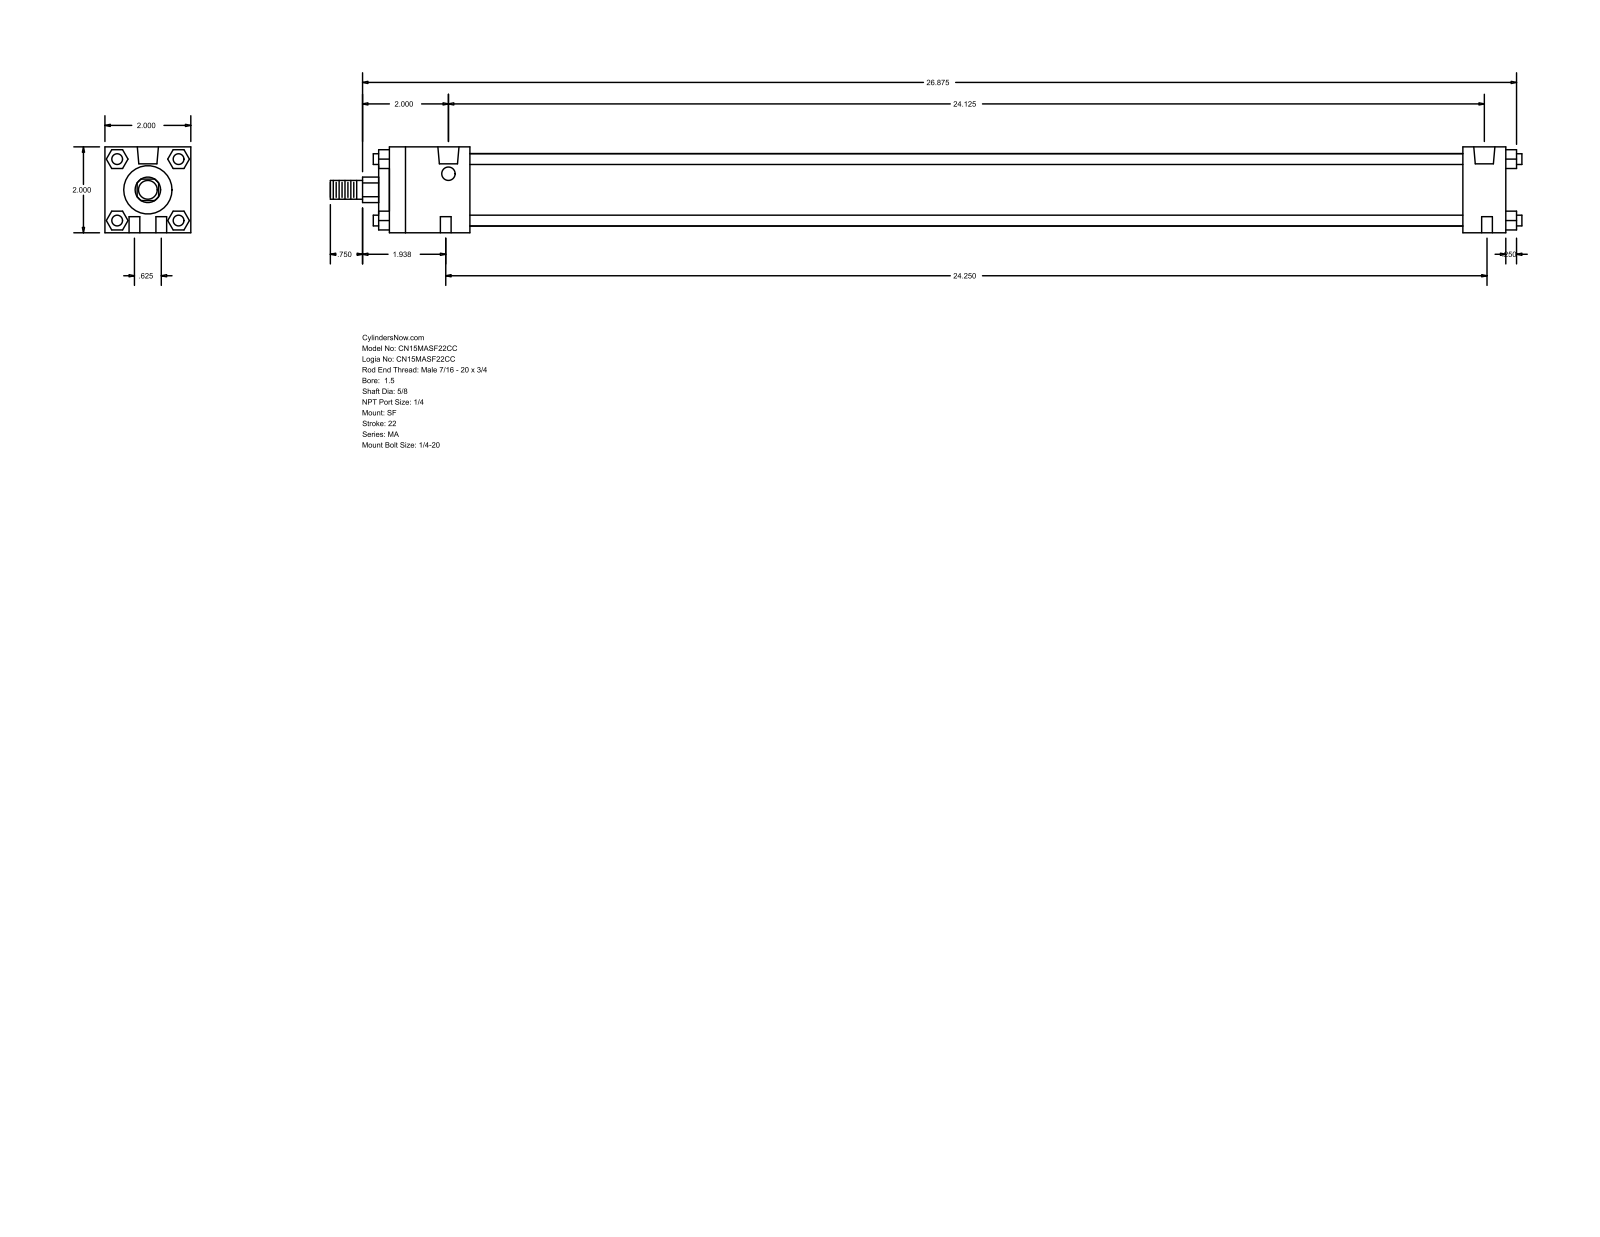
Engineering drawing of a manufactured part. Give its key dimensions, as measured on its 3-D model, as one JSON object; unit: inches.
{"part_name": "MA_SF__0150_0.625", "step_written_by": "GSSL Pune (CONFIG_CONTROL_DESIGN)", "units": "inches", "bodies": {"solids": 0, "faces": 124, "planar": 94, "cylindrical": 30, "other": 0}, "overall_size": [27.75, 2, 2], "round_holes": [[0.25, 4], [0.313, 2], [0.492, 2]], "round_bosses_or_shafts": [[0.25, 4], [1.69, 1], [1.125, 1], [0.625, 1], [0.437, 1]], "partial_cylinders_radius": [[0.297, 1]], "face_to_face_distances": [2, 26, 0.25, 26.25, 1.875, 25, 23.125, 24.125, 1, 2.125], "hole_center_spacings": [0.319, 0.625, 24.125, 24.189, 24.19, 24.25, 24.258]}
